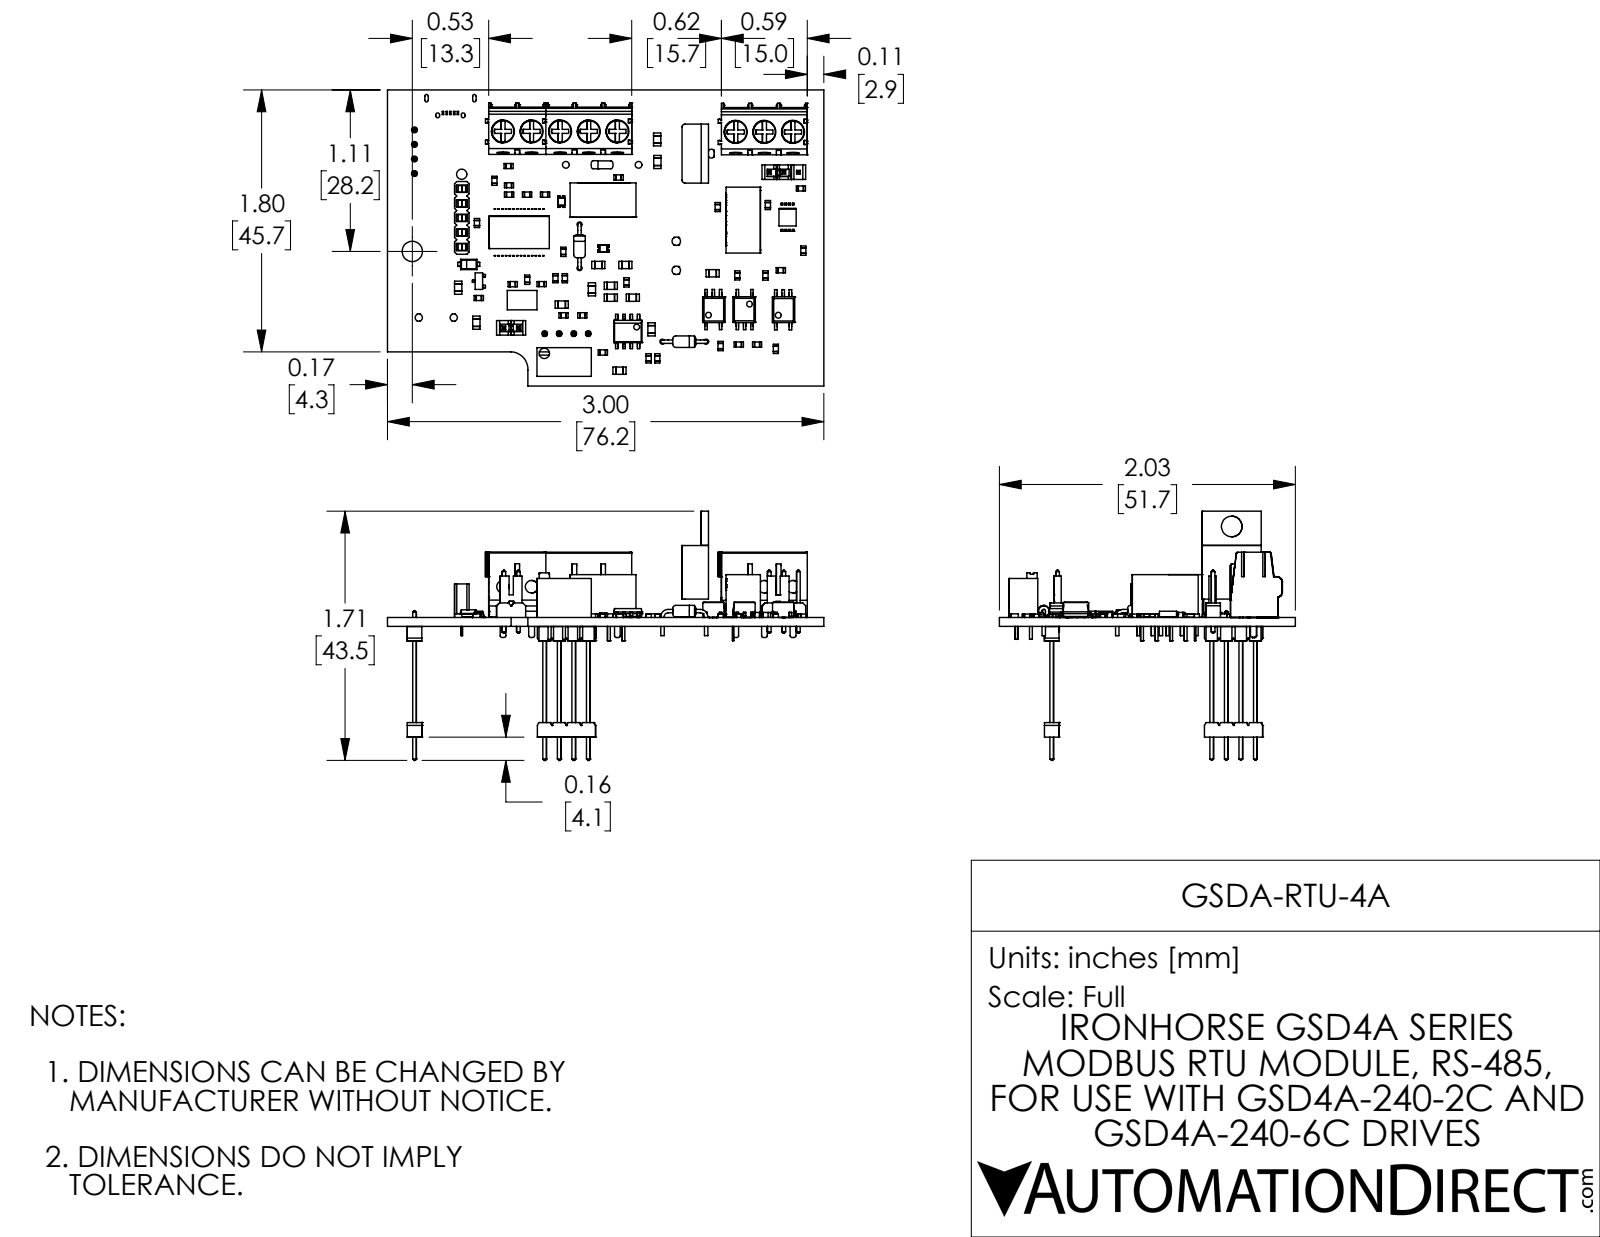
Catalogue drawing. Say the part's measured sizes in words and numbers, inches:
The part is named "GSDA-RTU-4A". Its 3-D file was written by "SolidWorks 2017 (AUTOMOTIVE_DESIGN)". It is 227 solids with 4003 faces: 3019 planar, 822 cylindrical and 162 other. Overall it measures 3 by 2.035 by 1.712 inches. Its volume is 0.695 cubic inches and its surface area 27.23 square inches. Round holes: 18 of diameter 0.04, 8 of diameter 0.087, 8 of diameter 0.157, 7 of diameter 0.055, 6 of diameter 0.031, 4 of diameter 0.035, 4 of diameter 0.04, 3 of diameter 0.033, 3 of diameter 0.043, 2 of diameter 0.03, 2 of diameter 0.047, 2 of diameter 0.058. Round bosses or shafts: 10 of diameter 0.039, 6 of diameter 0.024, 3 of diameter 0.018, 2 of diameter 0.079, 2 of diameter 0.079, 1 of diameter 0.071, 1 of diameter 0.02, 1 of diameter 0.019. Partial cylindrical surfaces (rounded edges, fillets, slot ends): 45 of radius 0.012, 30 of radius 0.006, 24 of radius 0.004, 12 of radius 0.008, 8 of radius 0.043, 8 of radius 0.059, 6 of radius 0.039, 4 of radius 0.005. The main face-to-face distances are 0.062, 0.022, 0.215, 0.062, 0.1, 0.04, 0.063, 0.235, 0.069, 0.193. The hole center spacings are 0.1, 0.197, 0.2, 1.207, 1.404, 0.393, 0.394, 0.59.
